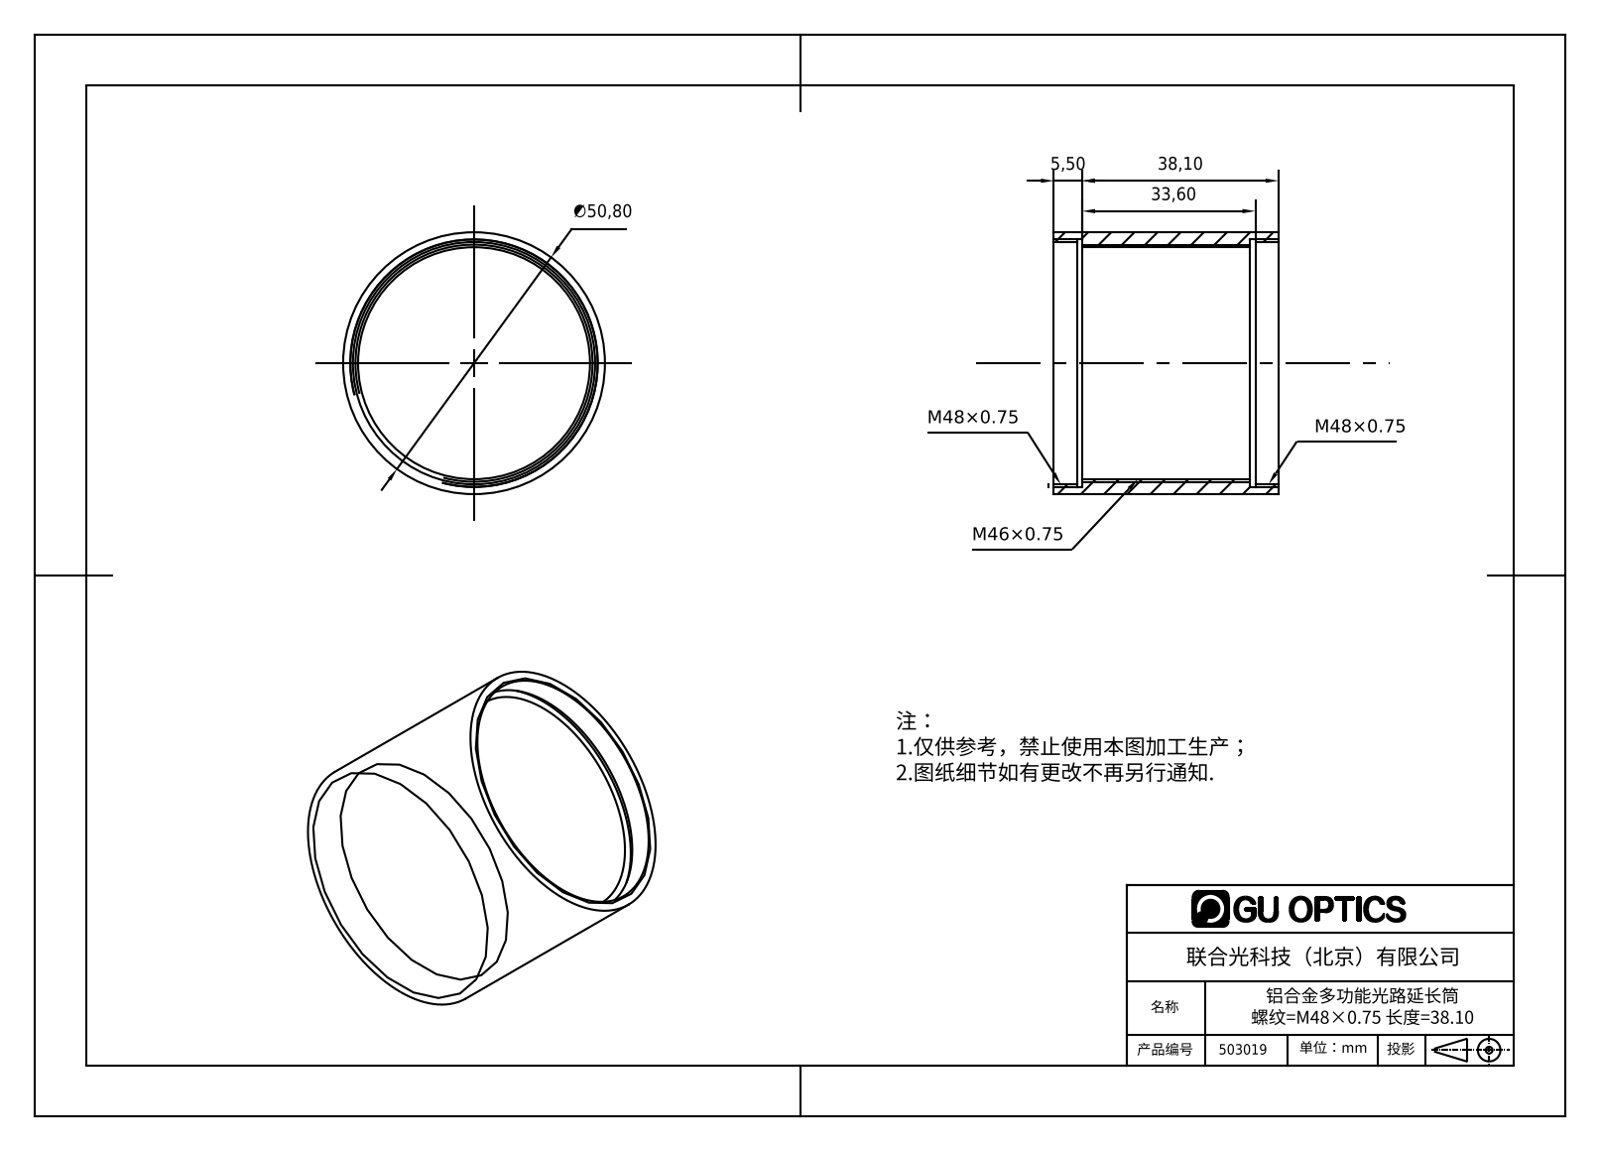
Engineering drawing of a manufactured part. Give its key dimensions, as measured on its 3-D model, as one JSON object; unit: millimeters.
{"part_name": "503019", "step_written_by": "SolidWorks 2016 (AUTOMOTIVE_DESIGN)", "units": "millimeters", "bodies": {"solids": 1, "faces": 18, "planar": 6, "cylindrical": 12, "other": 0}, "overall_size": [50.8, 50.8, 43.6], "volume_mm3": 17258, "surface_area_mm2": 14430, "round_holes": [[45, 1], [47, 1], [48.2, 1]], "round_bosses_or_shafts": [[50.8, 1]], "face_to_face_distances": [5.5, 38.1, 43.6, 32.6, 4.5, 39.1, 1, 33.6, 34.6]}
